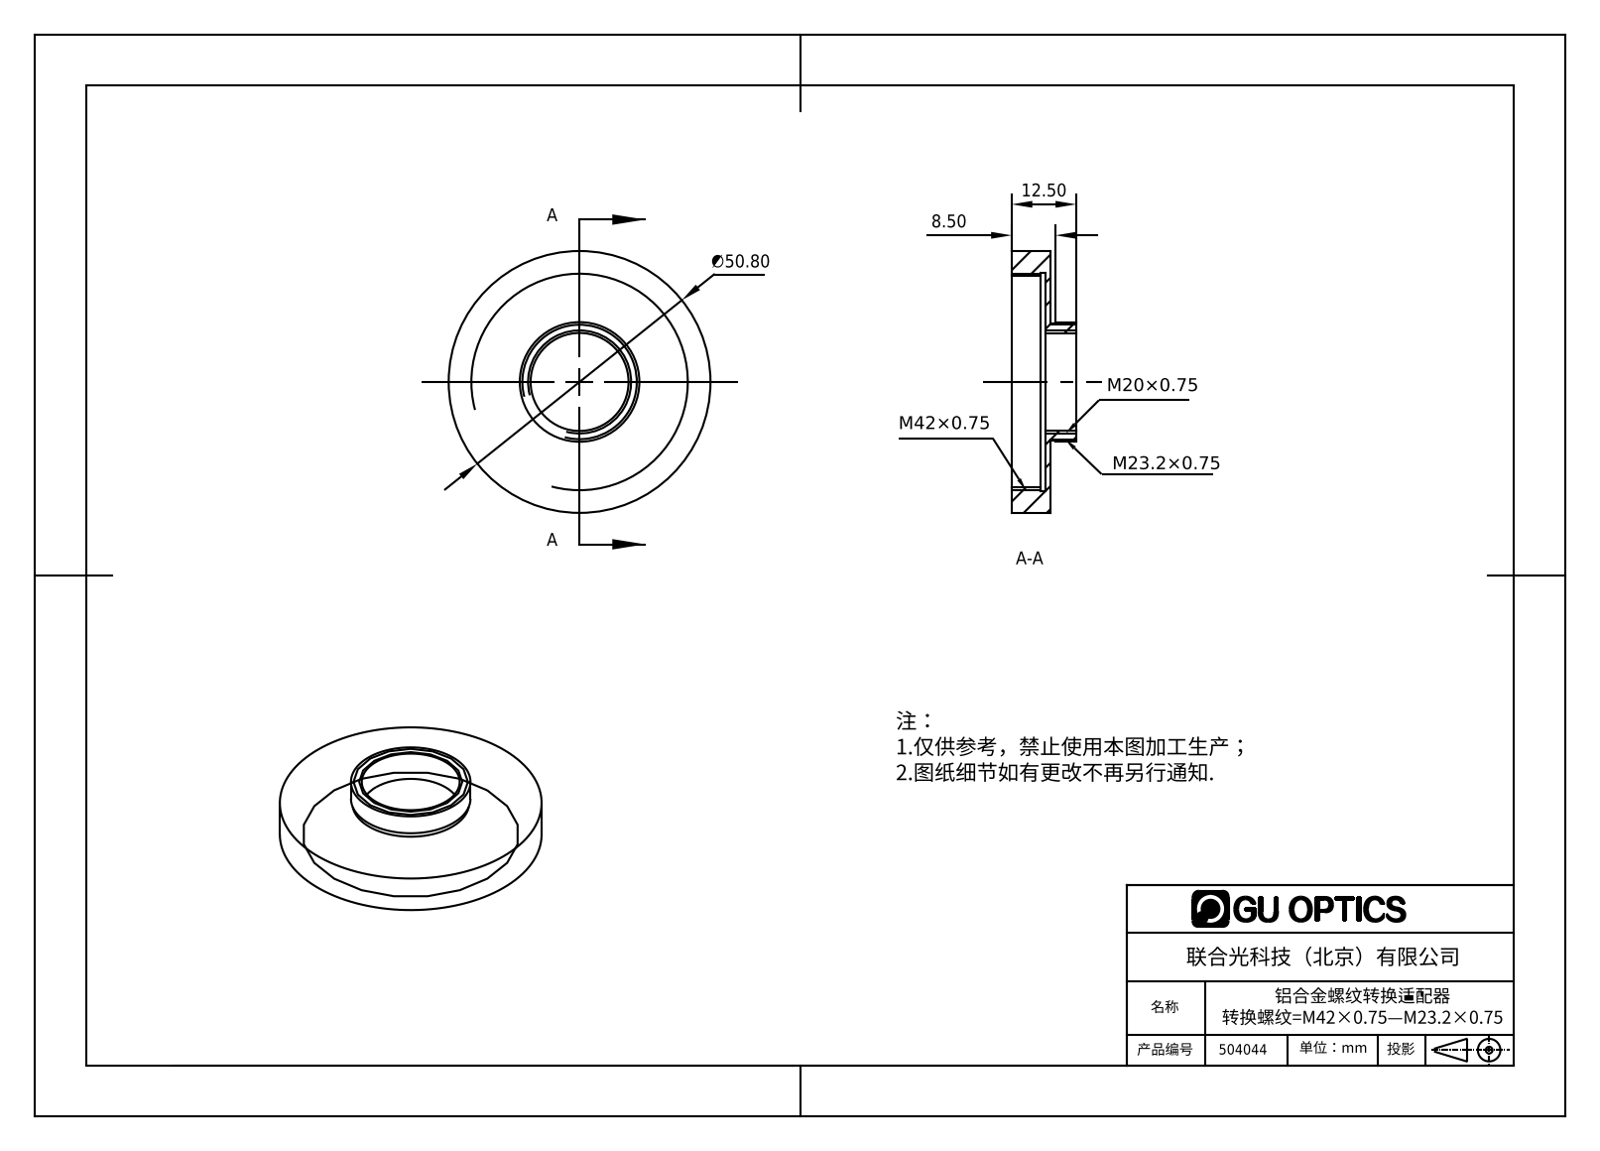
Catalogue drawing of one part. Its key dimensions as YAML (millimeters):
part_name: "504044"
step_written_by: "SolidWorks 2016 (AUTOMOTIVE_DESIGN)"
units: millimeters
bodies: {solids: 1, faces: 18, planar: 6, cylindrical: 12, other: 0}
overall_size: [50.8, 50.8, 12.5]
volume: 6936
surface_area: 6438
round_holes:
  - {diameter: 19, count: 1}
  - {diameter: 41, count: 1}
  - {diameter: 42.2, count: 1}
round_bosses_or_shafts:
  - {diameter: 50.8, count: 1}
  - {diameter: 23.2, count: 1}
  - {diameter: 22.7, count: 1}
face_to_face_distances: [1, 6.5, 7.5, 12.5, 6, 5, 2, 5.5, 7, 8.5]
